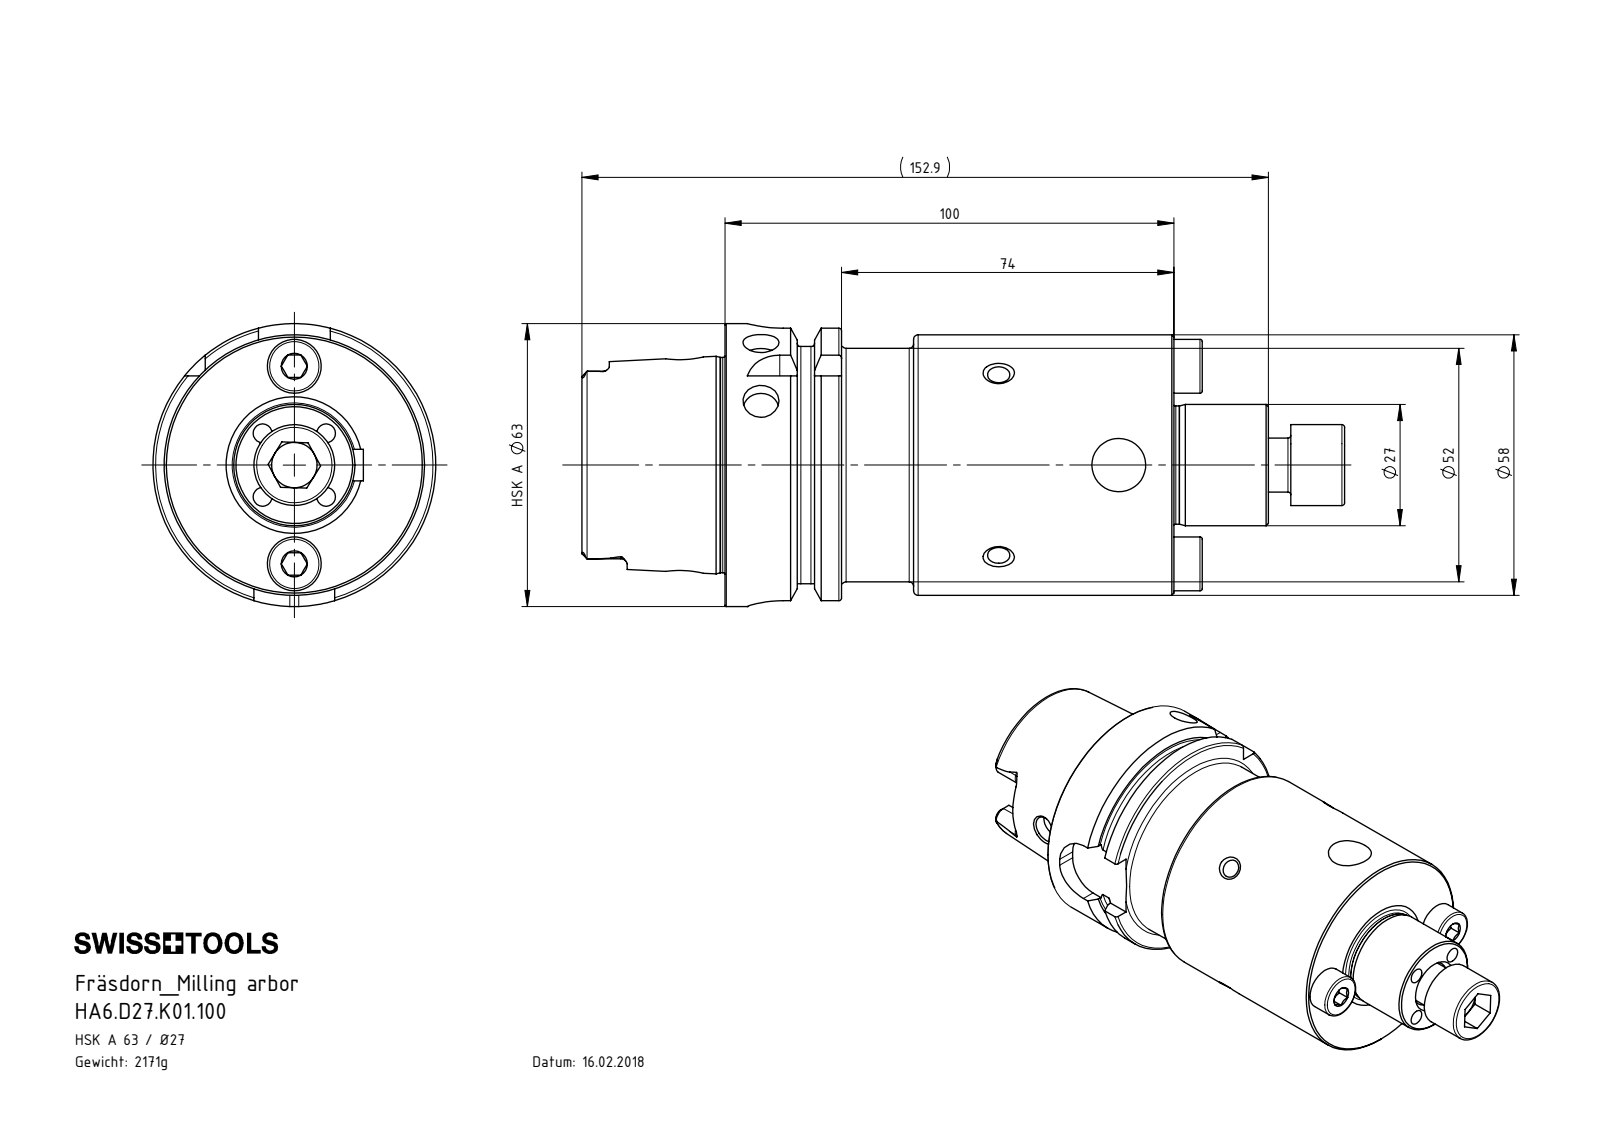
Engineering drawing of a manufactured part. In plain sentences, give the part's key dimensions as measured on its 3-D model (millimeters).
The part is named "HA6.D27.K01.100; D27-ER2.001.021_B; D27-ER3.001.016_A; D27-ER1.002.030_A (+1 more)". Its 3-D file was written by "SolidWorks 2017 (AUTOMOTIVE_DESIGN)". It is 5 solids with 390 faces: 97 planar, 119 cylindrical and 174 other. Overall it measures 169.9 by 63 by 63 millimeters. Its volume is 276 496 cubic millimeters and its surface area 49 740 square millimeters. Round holes: 6 of diameter 4.2, 6 of diameter 5, 3 of diameter 10, 2 of diameter 8, 1 of diameter 7.5, 1 of diameter 8.4, 1 of diameter 10.2, 1 of diameter 13, 1 of diameter 17, 1 of diameter 19, 1 of diameter 34, 1 of diameter 40. Round bosses or shafts: 3 of diameter 12, 2 of diameter 6, 2 of diameter 4.6, 1 of diameter 63, 1 of diameter 58, 1 of diameter 54.95, 1 of diameter 52, 1 of diameter 47.94. Partial cylindrical surfaces (rounded edges, fillets, slot ends): 6 of radius 1.4, 4 of radius 2.88, 4 of radius 8, 2 of radius 3.5, 2 of radius 4. The main face-to-face distances are 100, 16, 25.95, 74.05, 9.95, 90.05, 31.9, 41.85, 57.85, 131.9. The hole center spacings are 10, 14.14, 16.52, 29.05, 29.92, 20, 22, 44.
